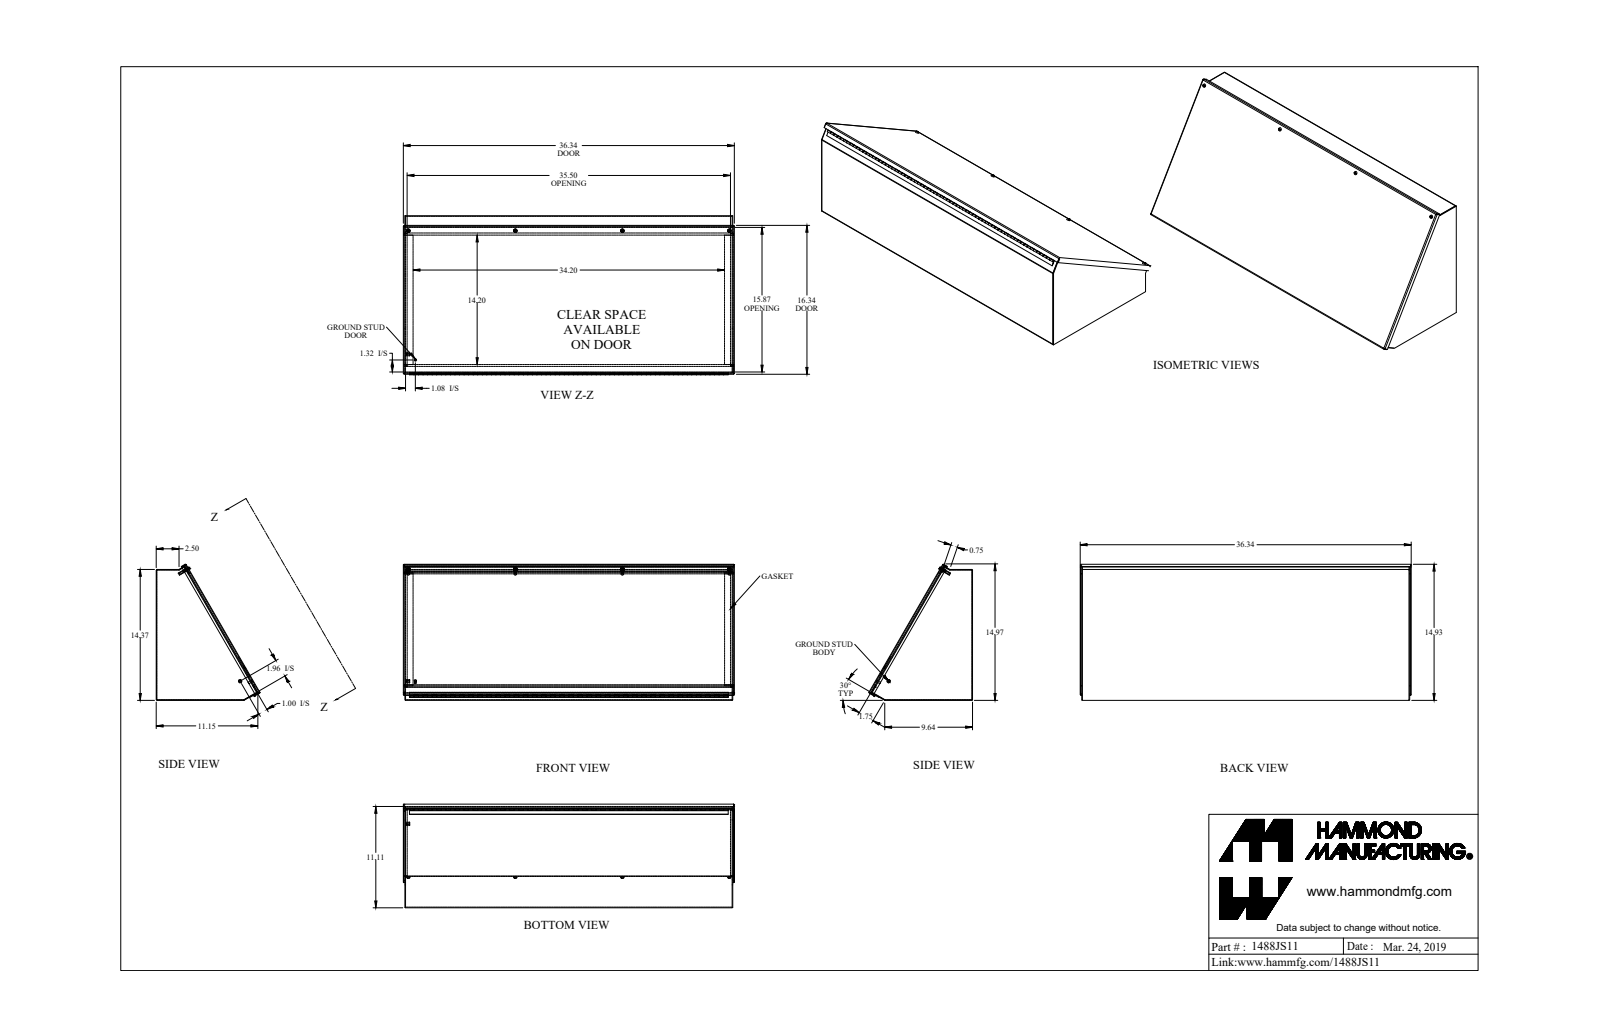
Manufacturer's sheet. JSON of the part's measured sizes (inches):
{"part_name": "1488JS11_Default", "step_written_by": "SolidWorks 2019 (CONFIG_CONTROL_DESIGN)", "units": "inches", "bodies": {"solids": 23, "faces": 994, "planar": 657, "cylindrical": 297, "other": 40}, "overall_size": [36.343, 14.933, 11.374], "volume_in3": 167, "surface_area_in2": 4258, "round_holes": [[0.159, 4], [0.25, 4], [0.156, 1]], "round_bosses_or_shafts": [[0.39, 4], [0.275, 4], [0.19, 4], [0.148, 4], [0.375, 1], [0.25, 1], [0.188, 1], [0.174, 1]], "partial_cylinders_radius": [[0.036, 12], [0.108, 12], [0.125, 4], [0.16, 4], [0.171, 4]], "face_to_face_distances": [0.072, 35.928, 14.293, 0.25, 35.856, 36, 0.322, 14.365, 14.221, 0.197], "hole_center_spacings": [11.75, 23.5, 11.75, 11.75, 35.25, 35.25, 23.5, 23.5]}
